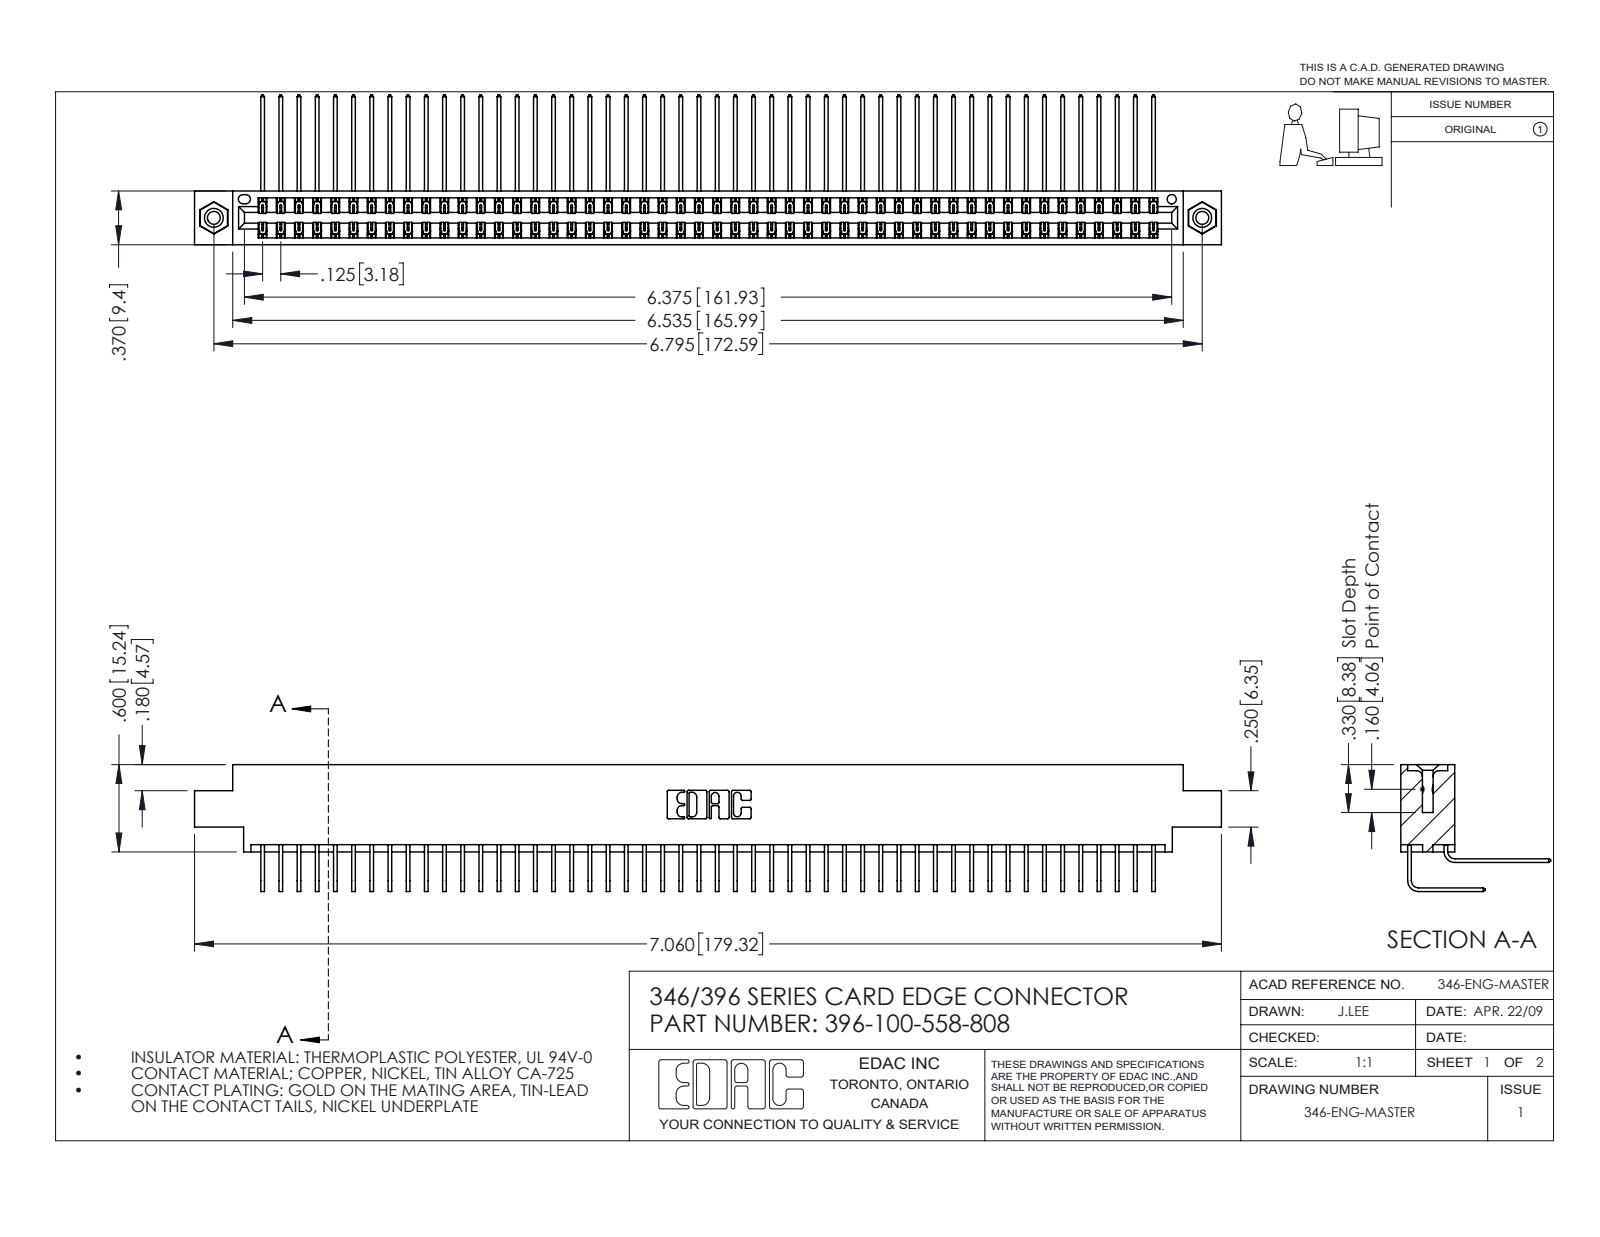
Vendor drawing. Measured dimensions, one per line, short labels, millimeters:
name: 345-250-001_345-250-003-102; 345-292-001_558 559 Tail - 1; 396-100-558-808; 346 Part_0.170 Offset - 0.156 Dia-TI (+1 more)
written by: SolidWorks 2016 (CONFIG_CONTROL_DESIGN)
unit: mm
bodies: 103 solids, 5586 faces (3812 planar, 1758 cylindrical, 16 other)
size: 179.3 × 26.2 × 22.2
volume: 17 960 mm³; area: 27 790 mm²
holes: 2× ⌀2.3, 2× ⌀3.2, 2× ⌀4, 1× ⌀1.6
bosses: 2× ⌀3.9
rounds: 150× R0.2, 22× R0.3, 6× R0.2, 6× R0.8, 3× R0.7, 2× R0.4, 2× R0.6, 2× R0.6
face distances: 8.2, 1.2, 0.6, 9.4, 6.4, 7.6, 1.8, 7, 5.6, 3.8
hole spacings: 6.2, 167.3, 172.6
